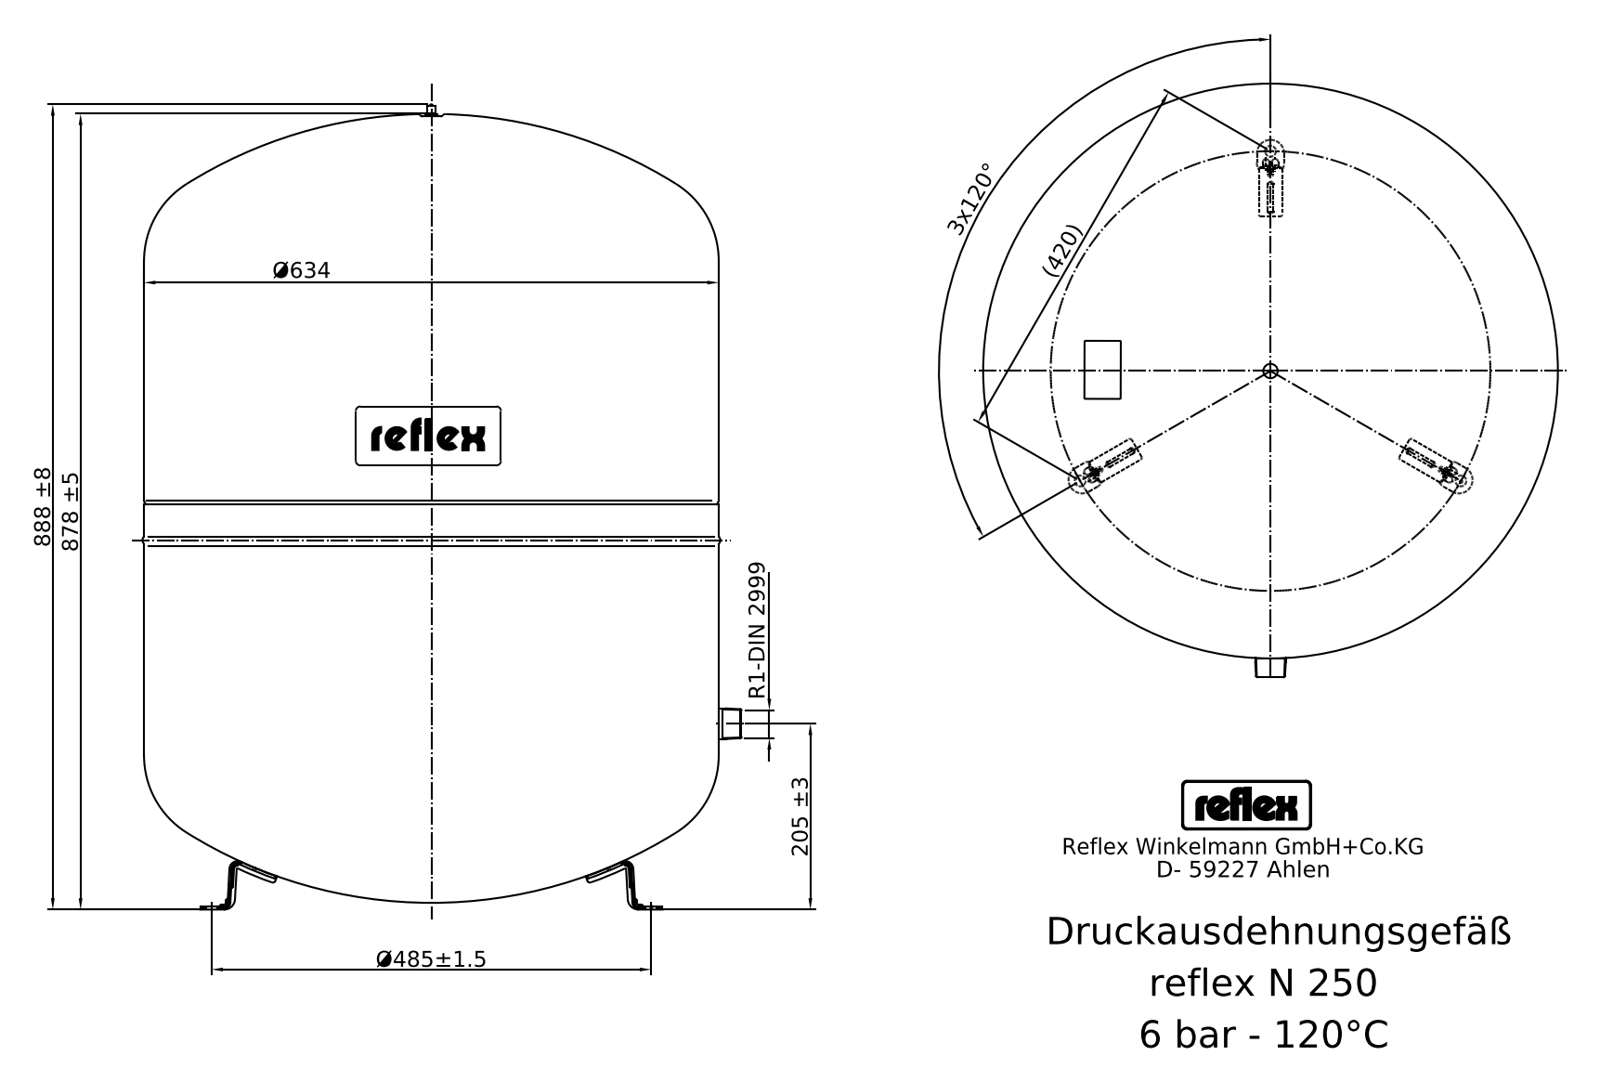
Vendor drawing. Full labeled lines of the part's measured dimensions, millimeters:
STEP written by: Mechanical Desktop 2008 (CONFIG_CONTROL_DESIGN)
Units: millimetres
Bodies: 16 solids, 245 faces (100 planar, 90 cylindrical, 55 other)
Overall size (bounding box): 915 × 664.46 × 644.91
Volume: 247 600 000 mm³ · Surface area: 3 416 000 mm²
Round holes (diameter × count): ⌀13.4 ×3, ⌀5.64 ×1, ⌀25.7 ×1
Round bosses / shafts (diameter × count): ⌀634.01 ×1, ⌀634 ×1, ⌀33.7 ×1, ⌀6.84 ×1, ⌀3.6 ×1, ⌀2.4 ×1
Partial cylindrical surfaces — rounded edges, fillets, slot ends (radius × count): R1 ×15, R2.5 ×15, R5 ×15, R3.94 ×4, R1.57 ×3, R2.69 ×2, R4.72 ×2, R6.49 ×2
Main face-to-face distances: 571, 2.5, 47.5, 285.5, 45, 50, 172, 457.5, 743, 2
Hole centre spacings: 242.5, 420.02
